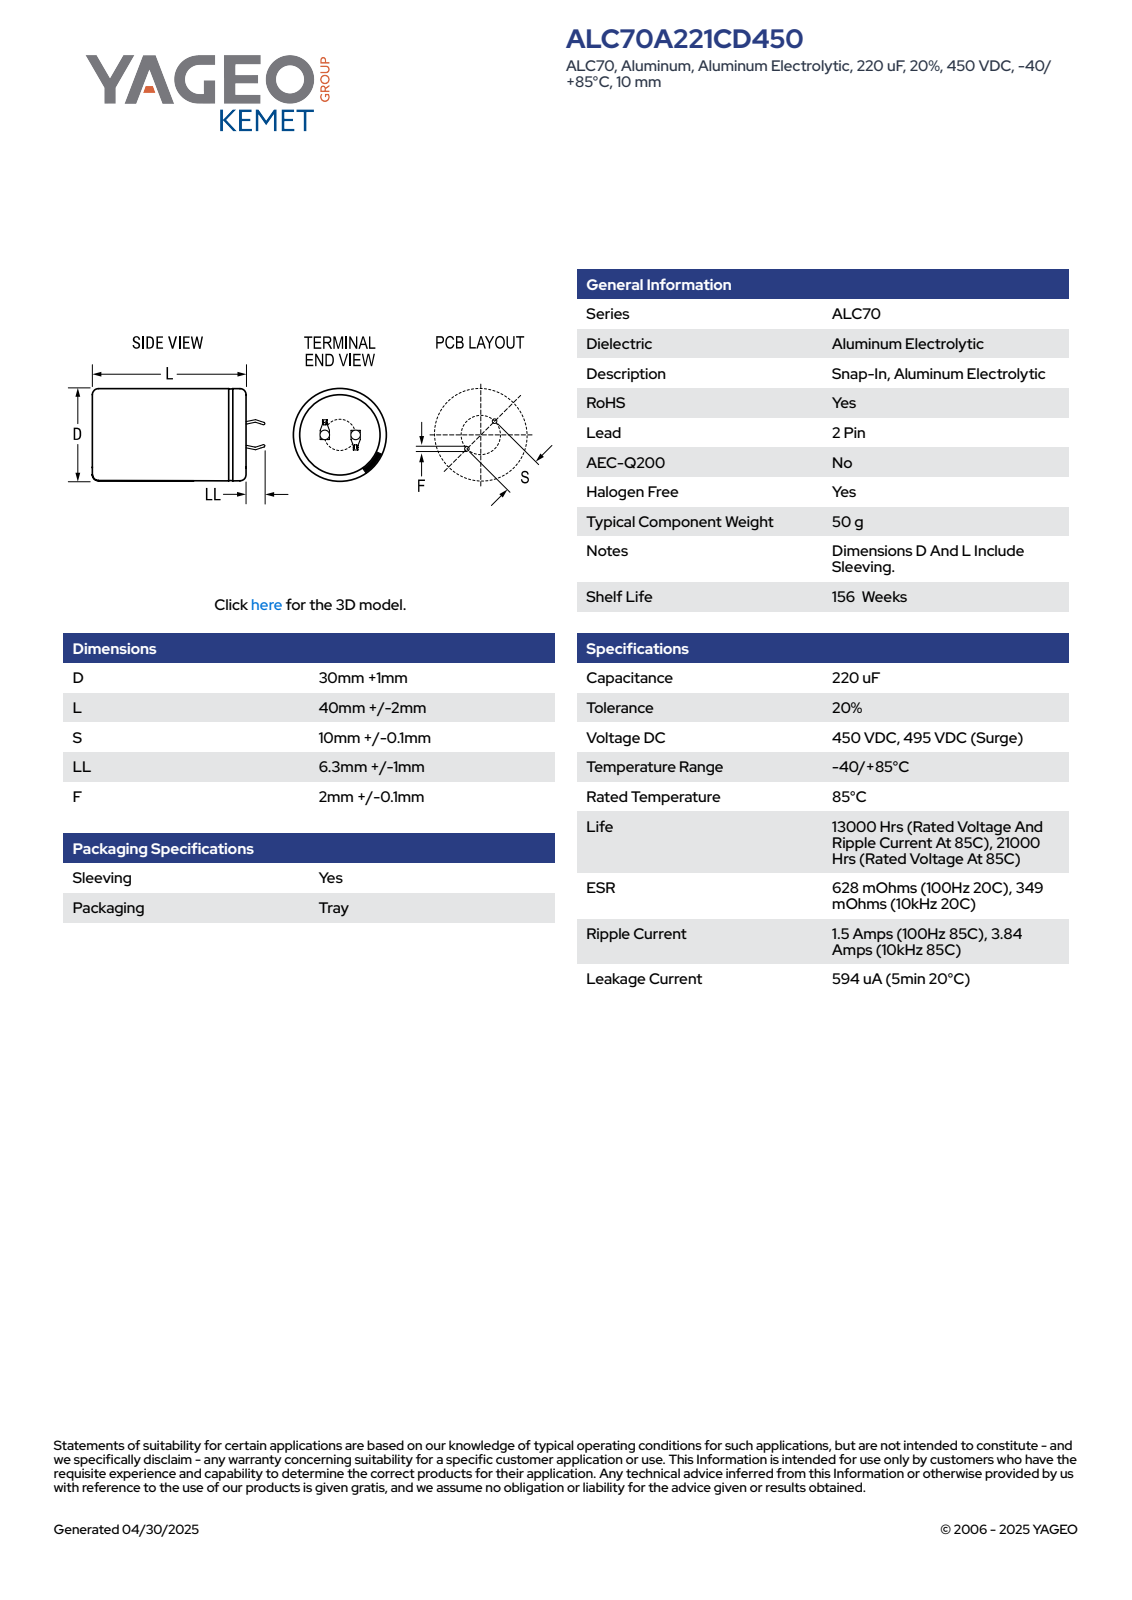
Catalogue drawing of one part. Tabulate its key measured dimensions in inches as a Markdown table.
| quantity | value |
| --- | --- |
| part name | CARS_K2P_30X40_D31L42S10LL7.3F2.1 |
| STEP written by | SolidWorks 2014 (AUTOMOTIVE_DESIGN) |
| units | inches |
| bodies | 1 solid, 100 faces (52 planar, 9 cylindrical, 39 other) |
| overall size | 1.941 × 1.22 × 1.22 |
| volume | 1.914 in³ |
| surface area | 8.696 in² |
| round holes (diameter × count) | 1.08 × 1 |
| round bosses / shafts (diameter × count) | 1.22 × 1 |
| partial cylindrical surfaces (radius × count) | 0.61 × 1 |
| main face-to-face distances | 1.653, 0.024, 1.673, 0.02, 0.279, 0.301, 0.03, 0.053, 0.302, 0.255 |
